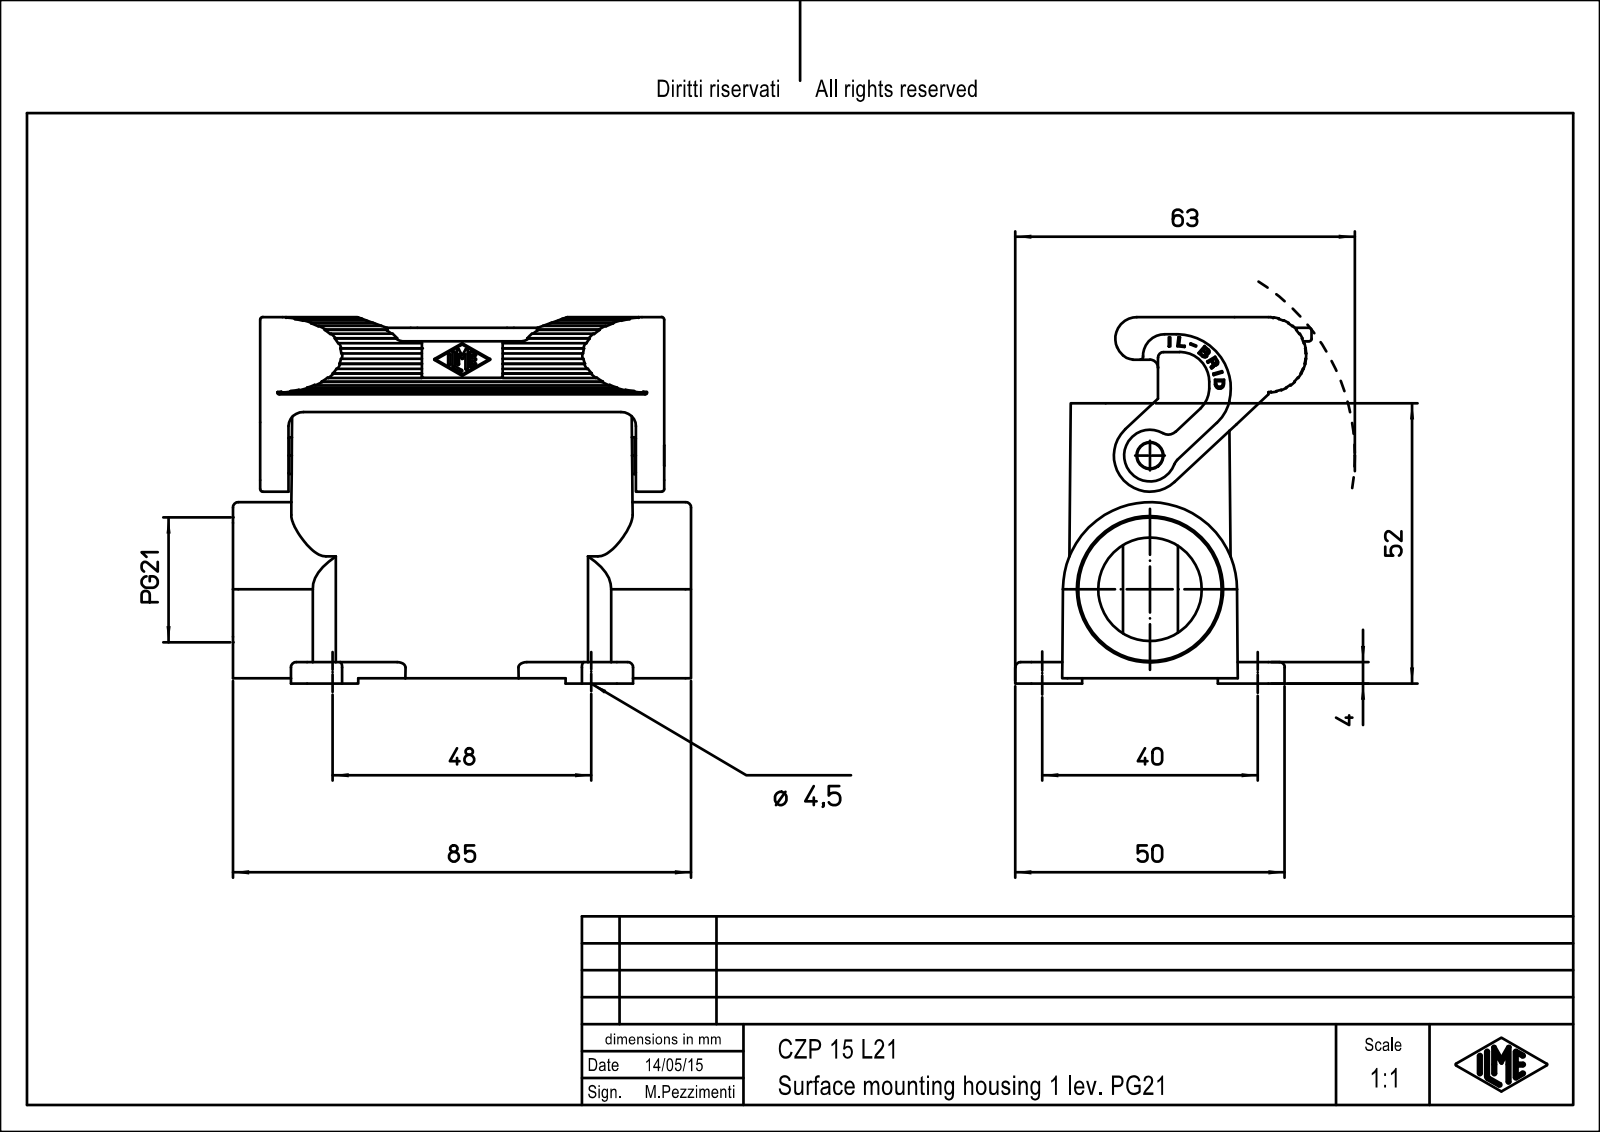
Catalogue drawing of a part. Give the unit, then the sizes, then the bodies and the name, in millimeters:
Units: millimetres
Overall size (bounding box): 85 × 69 × 53.9
Round holes (diameter × count): ⌀4.5 ×2, ⌀3.1 ×1, ⌀24.78 ×1, ⌀26.78 ×1
Round bosses / shafts (diameter × count): ⌀10 ×1, ⌀6.3 ×1, ⌀5 ×1, ⌀2.6 ×1, ⌀2.5 ×1
Partial cylindrical surfaces — rounded edges, fillets, slot ends (radius × count): R0.38 ×14, R1.5 ×6, R3 ×5, R6 ×5, R1 ×4, R1.4 ×3, R2.8 ×3, R0.5 ×2
Main face-to-face distances: 2.75, 27.25, 30, 24.5, 1.4, 3.5, 3.75, 1, 28.25, 31
Hole centre spacings: 47.12, 62.47
Volume: 45 362 mm³ · Surface area: 32 188 mm²
Bodies: 3 solids, 321 faces (116 planar, 78 cylindrical, 127 other)
Part name (STEP PRODUCT): CZ_MZ Gehäuse 1 Bügel
STEP written by: Autodesk Inventor 7 (AUTOMOTIVE_DESIGN)
